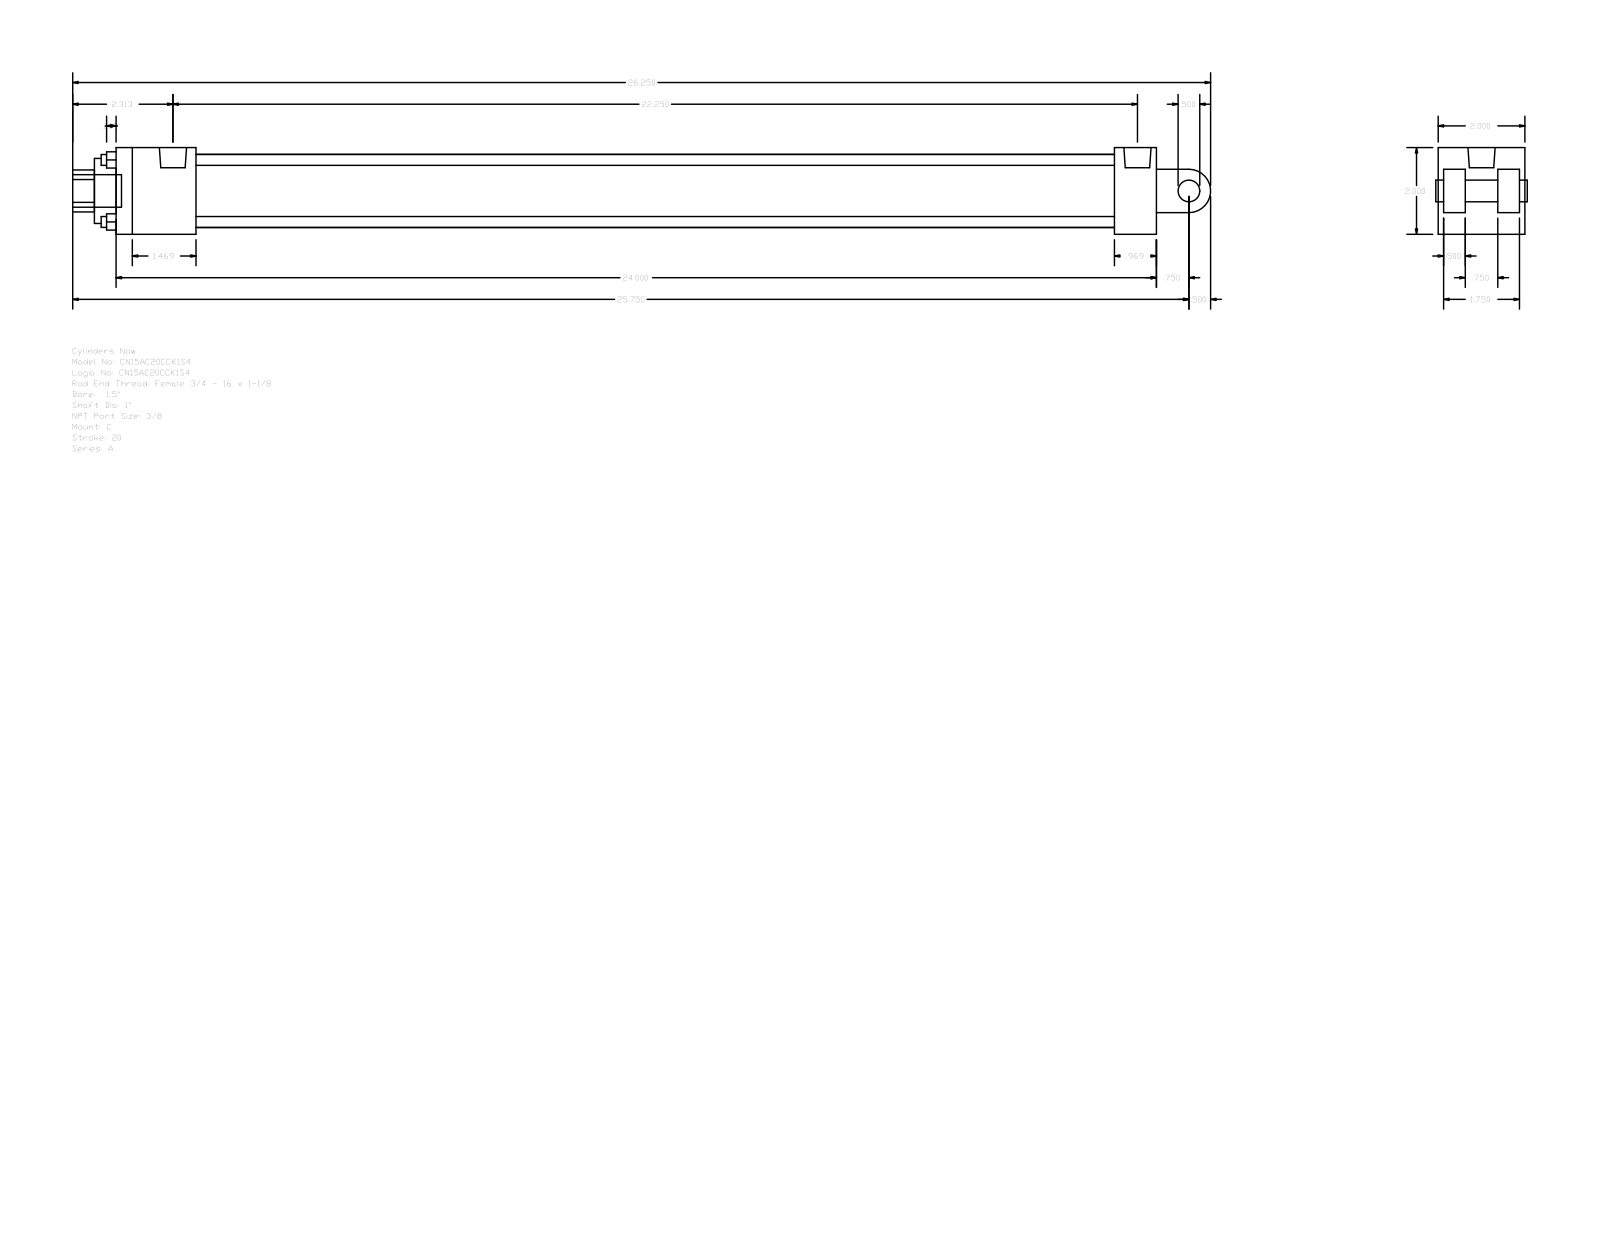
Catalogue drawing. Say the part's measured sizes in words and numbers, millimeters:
The part is named "A_C__0150_1". Its 3-D file was written by "GSSL Pune (CONFIG_CONTROL_DESIGN)". It is 0 solids with 99 faces: 70 planar, 29 cylindrical and 0 other. Overall it measures 666.75 by 50.8 by 50.8 millimeters. Round holes: 4 of diameter 6.35, 2 of diameter 5.56, 1 of diameter 15.93, 1 of diameter 25.4, 1 of diameter 38.1, 1 of diameter 42.93. Round bosses or shafts: 2 of diameter 5.56, 1 of diameter 19.05, 1 of diameter 15.93, 1 of diameter 12.7. Partial cylindrical surfaces (rounded edges, fillets, slot ends): 1 of radius 12.29, 1 of radius 12.7. The main face-to-face distances are 50.8, 12.7, 3.17, 15.87, 47.63, 34.93, 31.76, 609.6, 584.99, 24.61. The hole center spacings are 25.68, 36.32, 51.36, 3.97.
